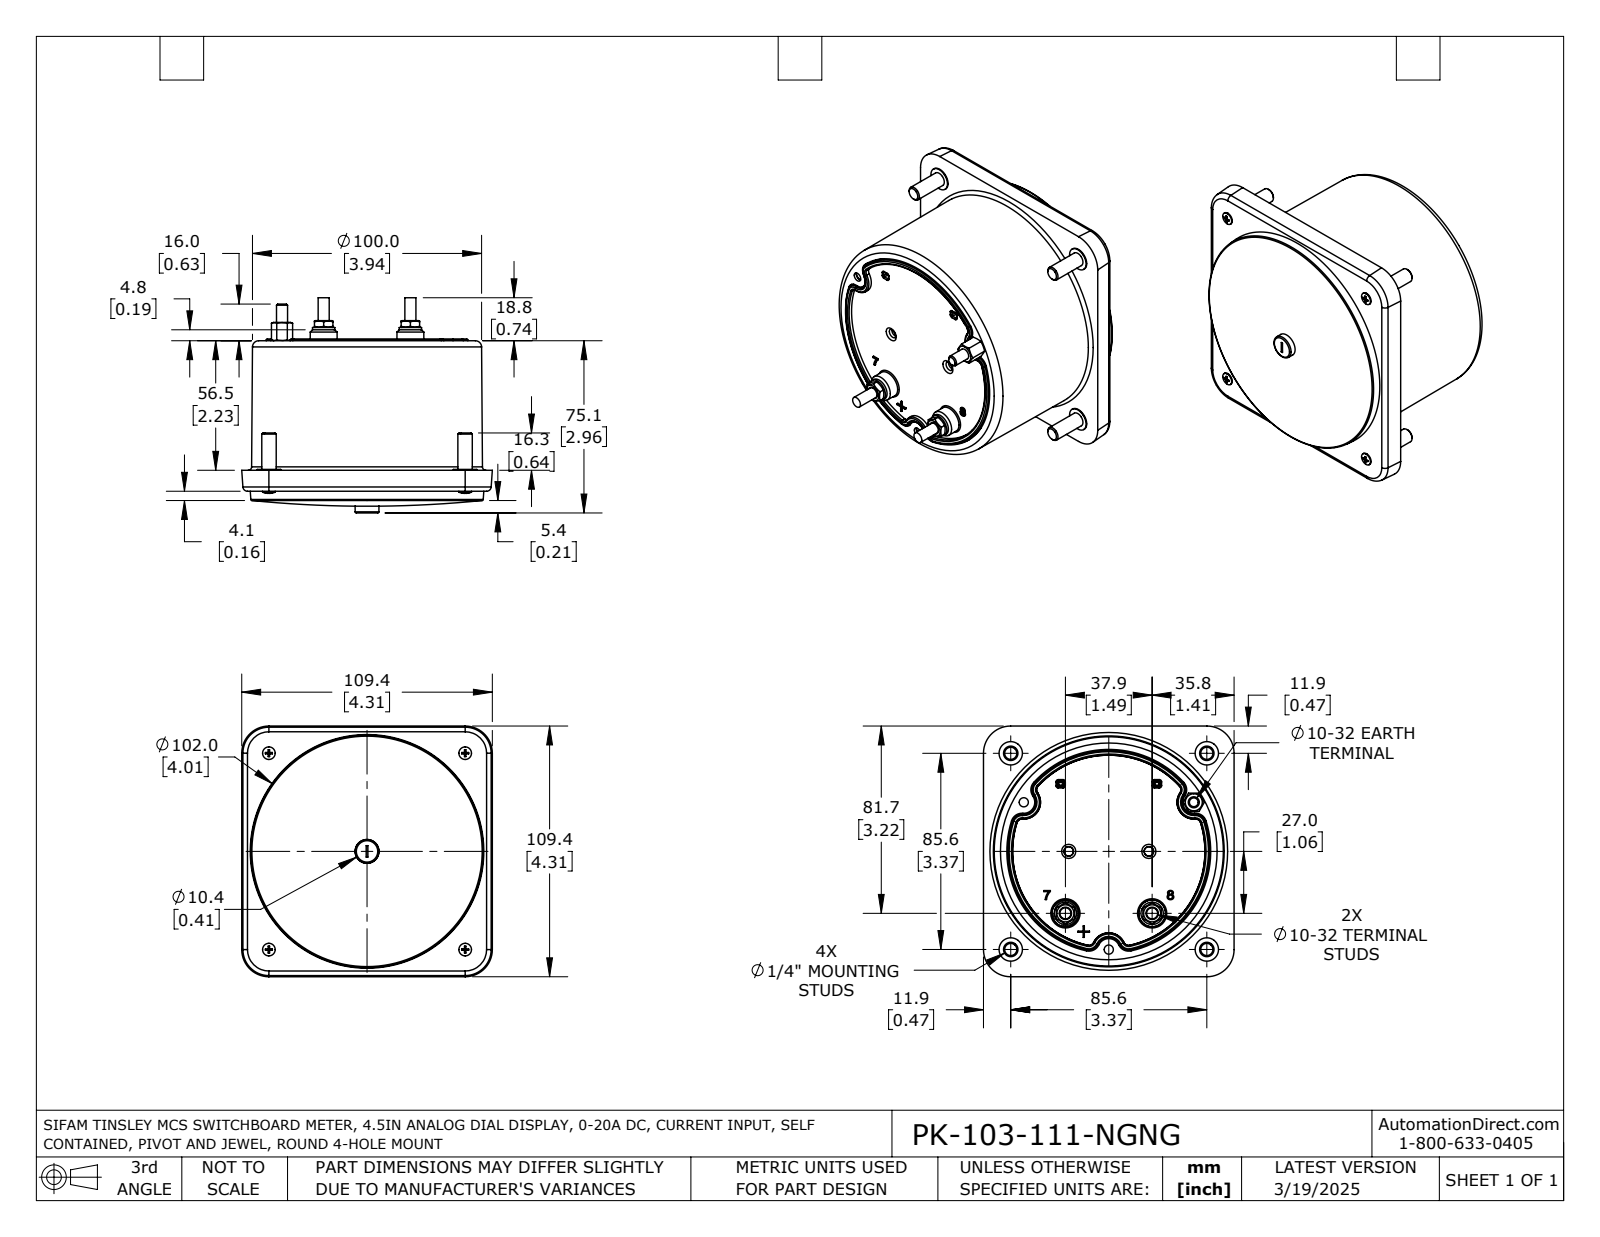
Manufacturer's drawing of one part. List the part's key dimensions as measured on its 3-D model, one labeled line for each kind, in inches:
Part name (STEP PRODUCT): PK-103-111-NGNG
STEP written by: SolidWorks 2021 (AUTOMOTIVE_DESIGN)
Units: inches
Bodies: 1 solid, 609 faces (167 planar, 141 cylindrical, 301 other)
Overall size (bounding box): 4.307 × 4.307 × 3.697
Volume: 36.28 in³ · Surface area: 82.21 in²
Round holes (diameter × count): ⌀0.094 ×4, ⌀0.138 ×4, ⌀0.315 ×4, ⌀0.157 ×3, ⌀0.209 ×2
Round bosses / shafts (diameter × count): ⌀0.402 ×4, ⌀0.248 ×4, ⌀0.217 ×4, ⌀0.114 ×4, ⌀0.19 ×3, ⌀0.384 ×2, ⌀0.146 ×1
Partial cylindrical surfaces — rounded edges, fillets, slot ends (radius × count): R0.02 ×24, R0.189 ×9, R0.079 ×4, R1.752 ×1
Main face-to-face distances: 2.177, 2.537, 0.36, 0.048, 2.225, 2.585, 0.489, 2.715, 2.667, 0.129
Hole centre spacings: 3.372, 3.37, 3.374, 3.378, 3.38, 4.769, 0.971, 1.126
